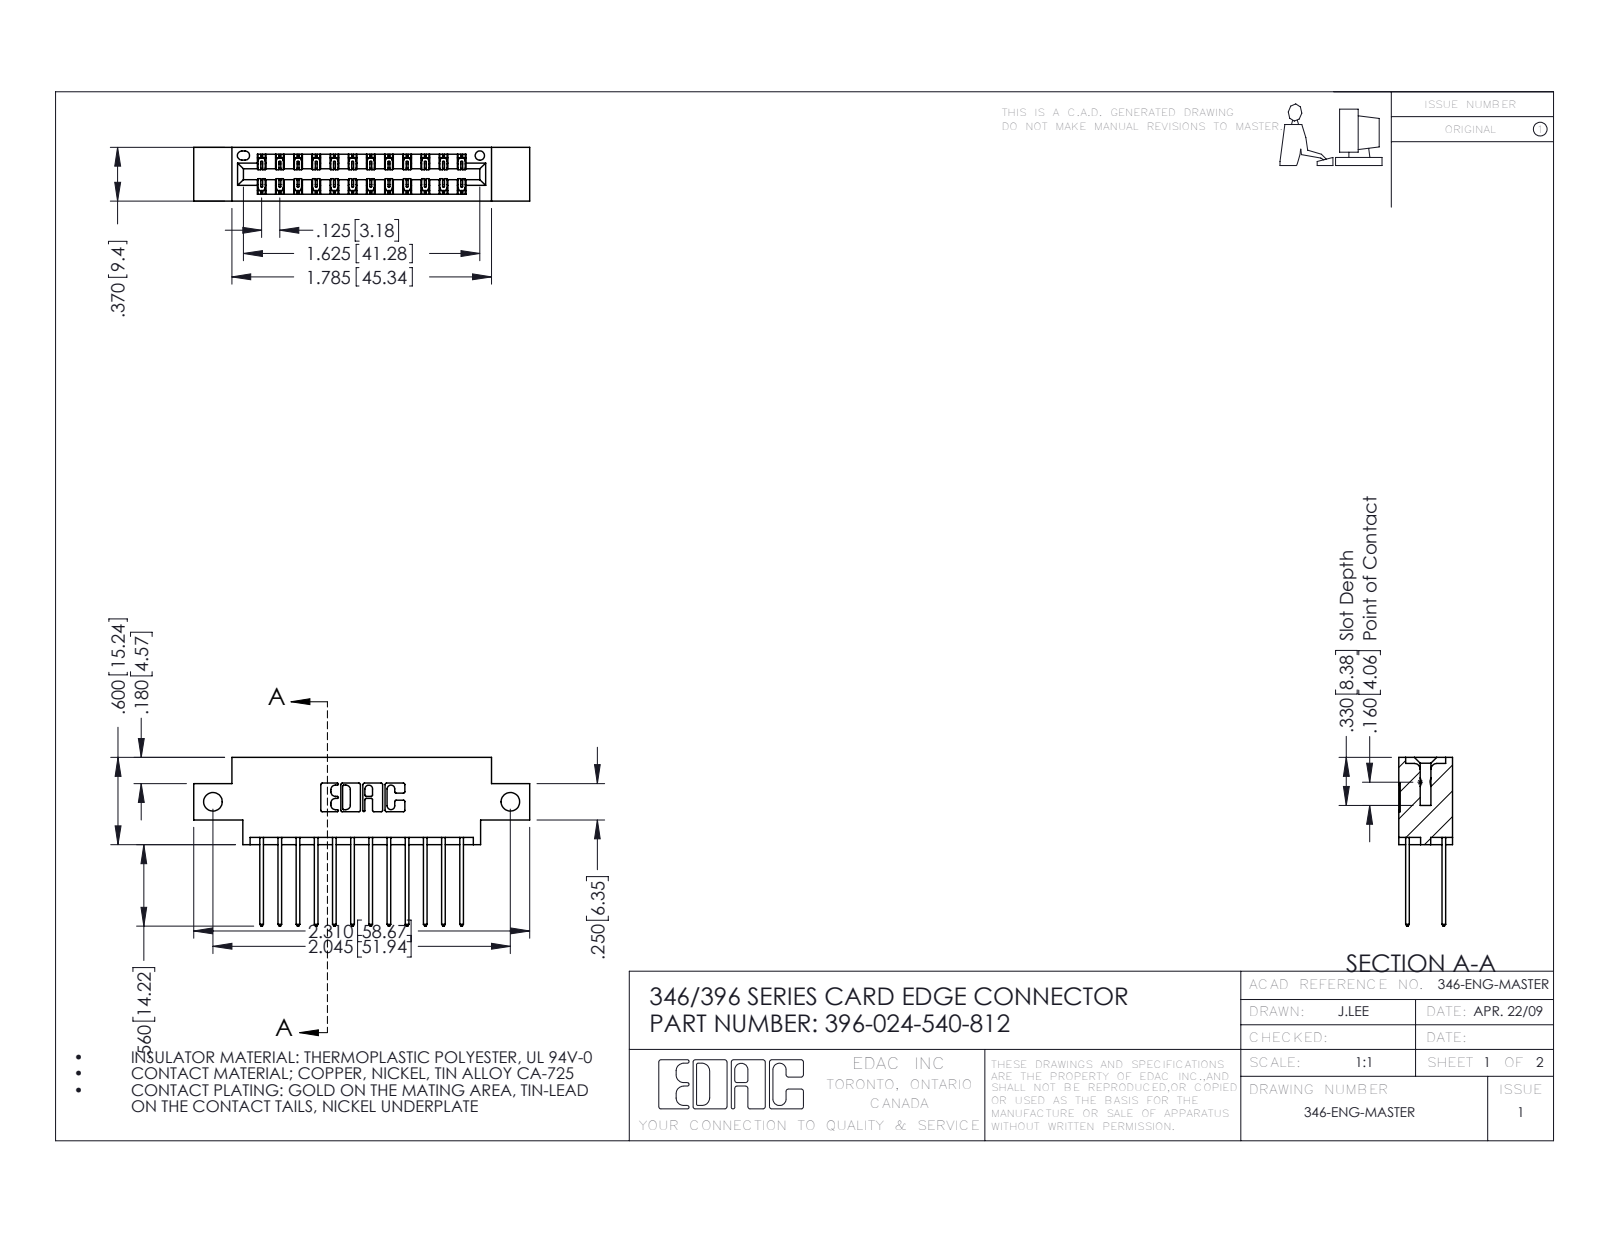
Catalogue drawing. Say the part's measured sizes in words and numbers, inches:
The part is named "346 Part_0.170 Offset - Side Mount; 345-292-001_345-293-140; 396-024-540-812". Its 3-D file was written by "SolidWorks 2016 (CONFIG_CONTROL_DESIGN)". It is 25 solids with 1374 faces: 920 planar, 454 cylindrical and 0 other. Overall it measures 2.31 by 1.16 by 0.37 inches. Its volume is 0.326 cubic inches and its surface area 11.37 square inches. Round holes: 2 of diameter 0.128, 1 of diameter 0.064. Partial cylindrical surfaces (rounded edges, fillets, slot ends): 36 of radius 0.006, 24 of radius 0.01, 22 of radius 0.01, 6 of radius 0.007, 6 of radius 0.031, 3 of radius 0.026, 2 of radius 0.014, 2 of radius 0.022. The main face-to-face distances are 0.25, 0.048, 0.322, 0.37, 0.072, 0.298, 0.025, 0.275, 0.148, 0.222. The hole center spacings are 2.045.
